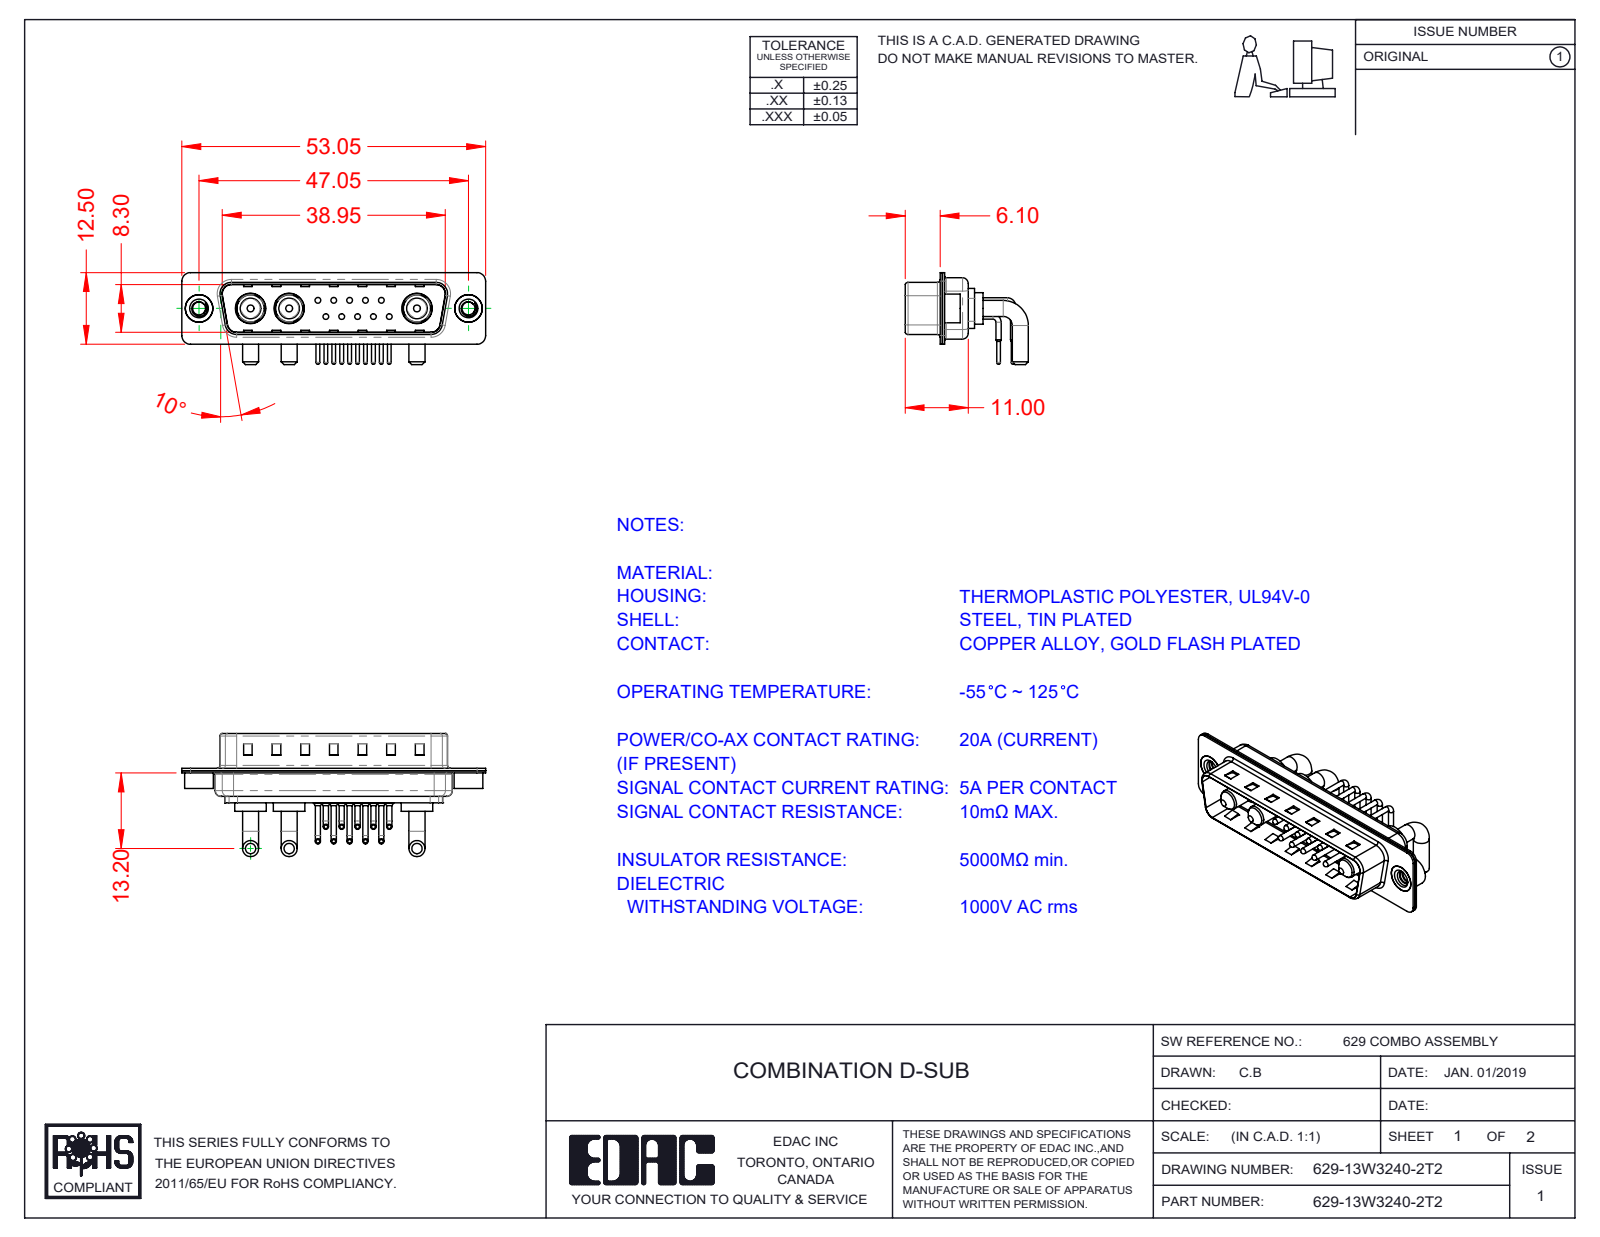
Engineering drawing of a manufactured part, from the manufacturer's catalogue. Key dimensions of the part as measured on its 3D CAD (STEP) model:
Part name (STEP PRODUCT): 629Combo Shell Front_25 Contacts; Power Pin_20A RA; 629-13W3240-2T2; 629Combo Contact Row 2 (+4 more)
STEP written by: SolidWorks 2020 (CONFIG_CONTROL_DESIGN)
Units: millimetres
Bodies: 21 solids, 1605 faces (841 planar, 560 cylindrical, 204 other)
Overall size (bounding box): 53.05 × 21.5 × 16.05
Volume: 3 211 mm³ · Surface area: 7 371 mm²
Round holes (diameter × count): ⌀0.75 ×10, ⌀1.6 ×10, ⌀2 ×10, ⌀4.85 ×3, ⌀5.3 ×3, ⌀2.26 ×2, ⌀4 ×2, ⌀4.8 ×2
Round bosses / shafts (diameter × count): ⌀0.9 ×20, ⌀1.5 ×10, ⌀1 ×10, ⌀0.65 ×10, ⌀2.8 ×6, ⌀5.5 ×3, ⌀5.2 ×3, ⌀4.75 ×3
Partial cylindrical surfaces — rounded edges, fillets, slot ends (radius × count): R1.5 ×16, R2 ×12, R1.01 ×10, R0.5 ×8, R1.6 ×8, R0.25 ×4, R0.6 ×4, R0.65 ×4
Main face-to-face distances: 0.4, 0.8, 9.5, 9.1, 8.7, 9.9, 5.6, 0.75, 1.2, 0.35
Hole centre spacings: 3.16, 2.77, 5.04, 5.54, 7.49, 5.03, 8.31, 10.11
